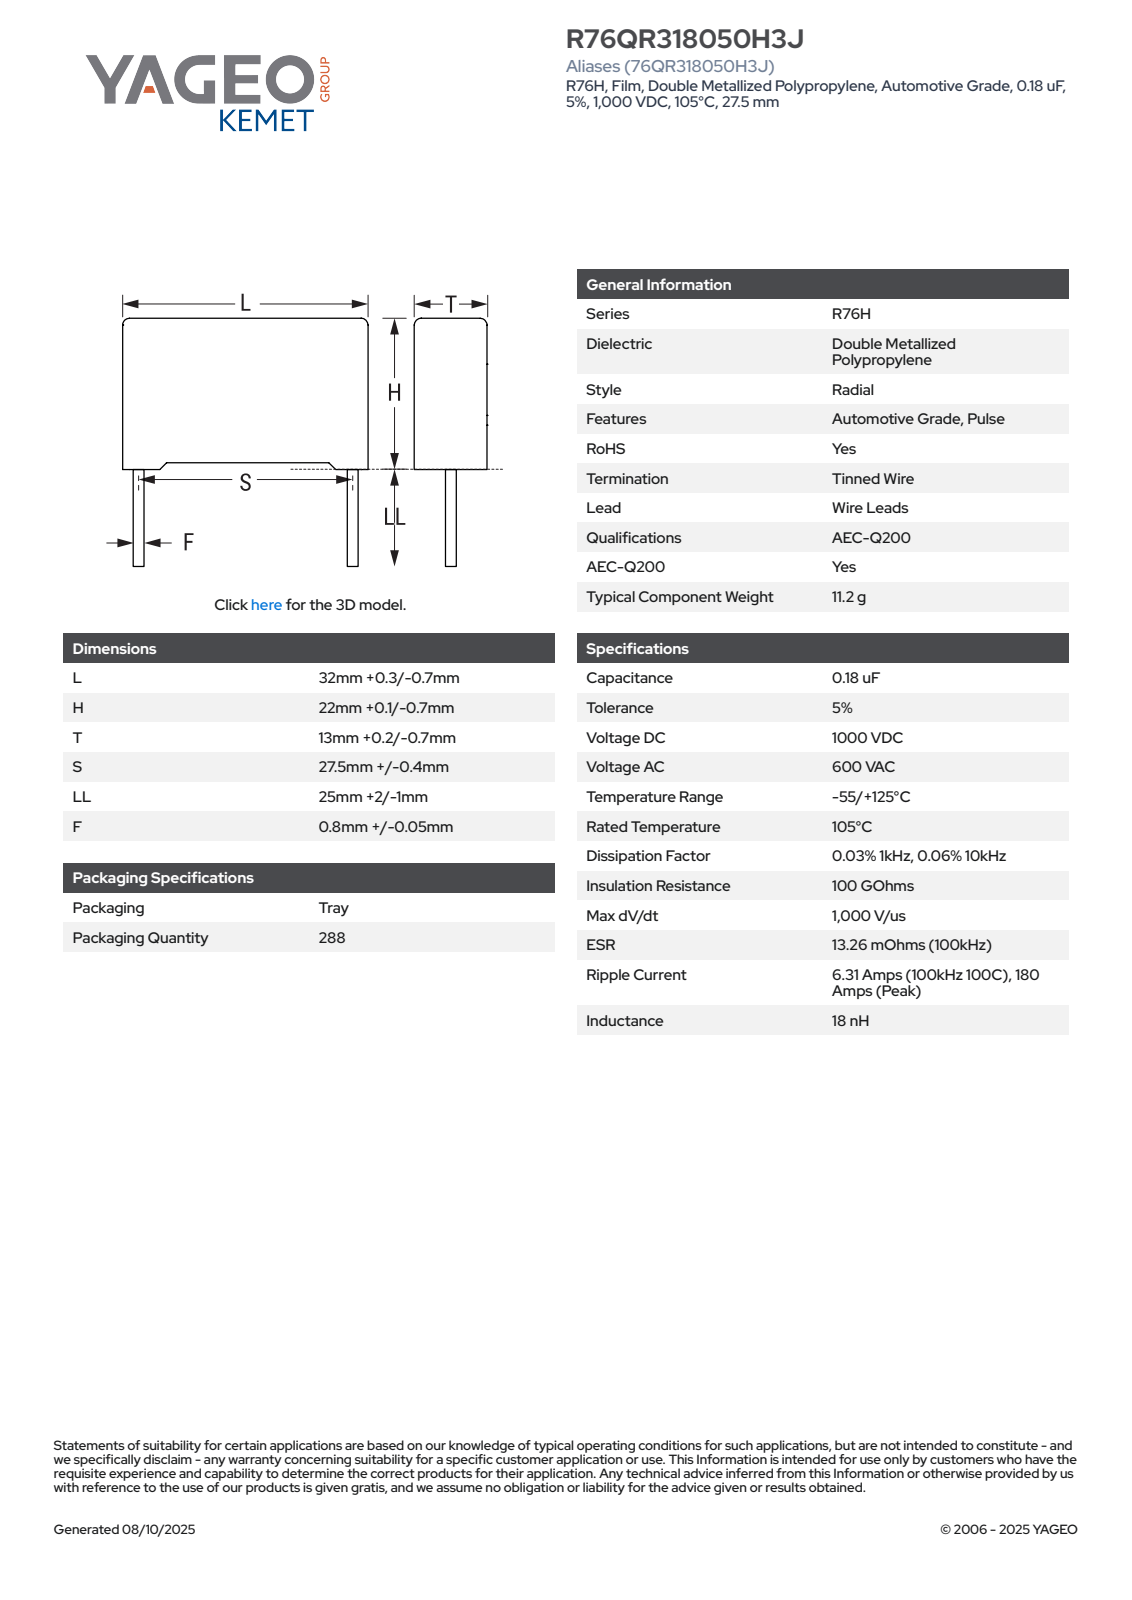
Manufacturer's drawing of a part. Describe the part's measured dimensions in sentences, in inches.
The part is named "CFR_RB2R76_32X22X13_L32.3H22.1T13.2S27.5LL27F0.85". Its 3-D file was written by "SolidWorks 2014 (AUTOMOTIVE_DESIGN)". It is 4 solids with 85 faces: 77 planar, 8 cylindrical and 0 other. Overall it measures 1.933 by 1.272 by 0.52 inches. Its volume is 0.559 cubic inches and its surface area 4.746 square inches. Round bosses or shafts: 2 of diameter 0.033. Partial cylindrical surfaces (rounded edges, fillets, slot ends): 4 of radius 0.02. The main face-to-face distances are 0.52, 0.84, 1.272, 0.841, 0.03, 0.03, 0.87, 0.043, 0.52, 1.229.
